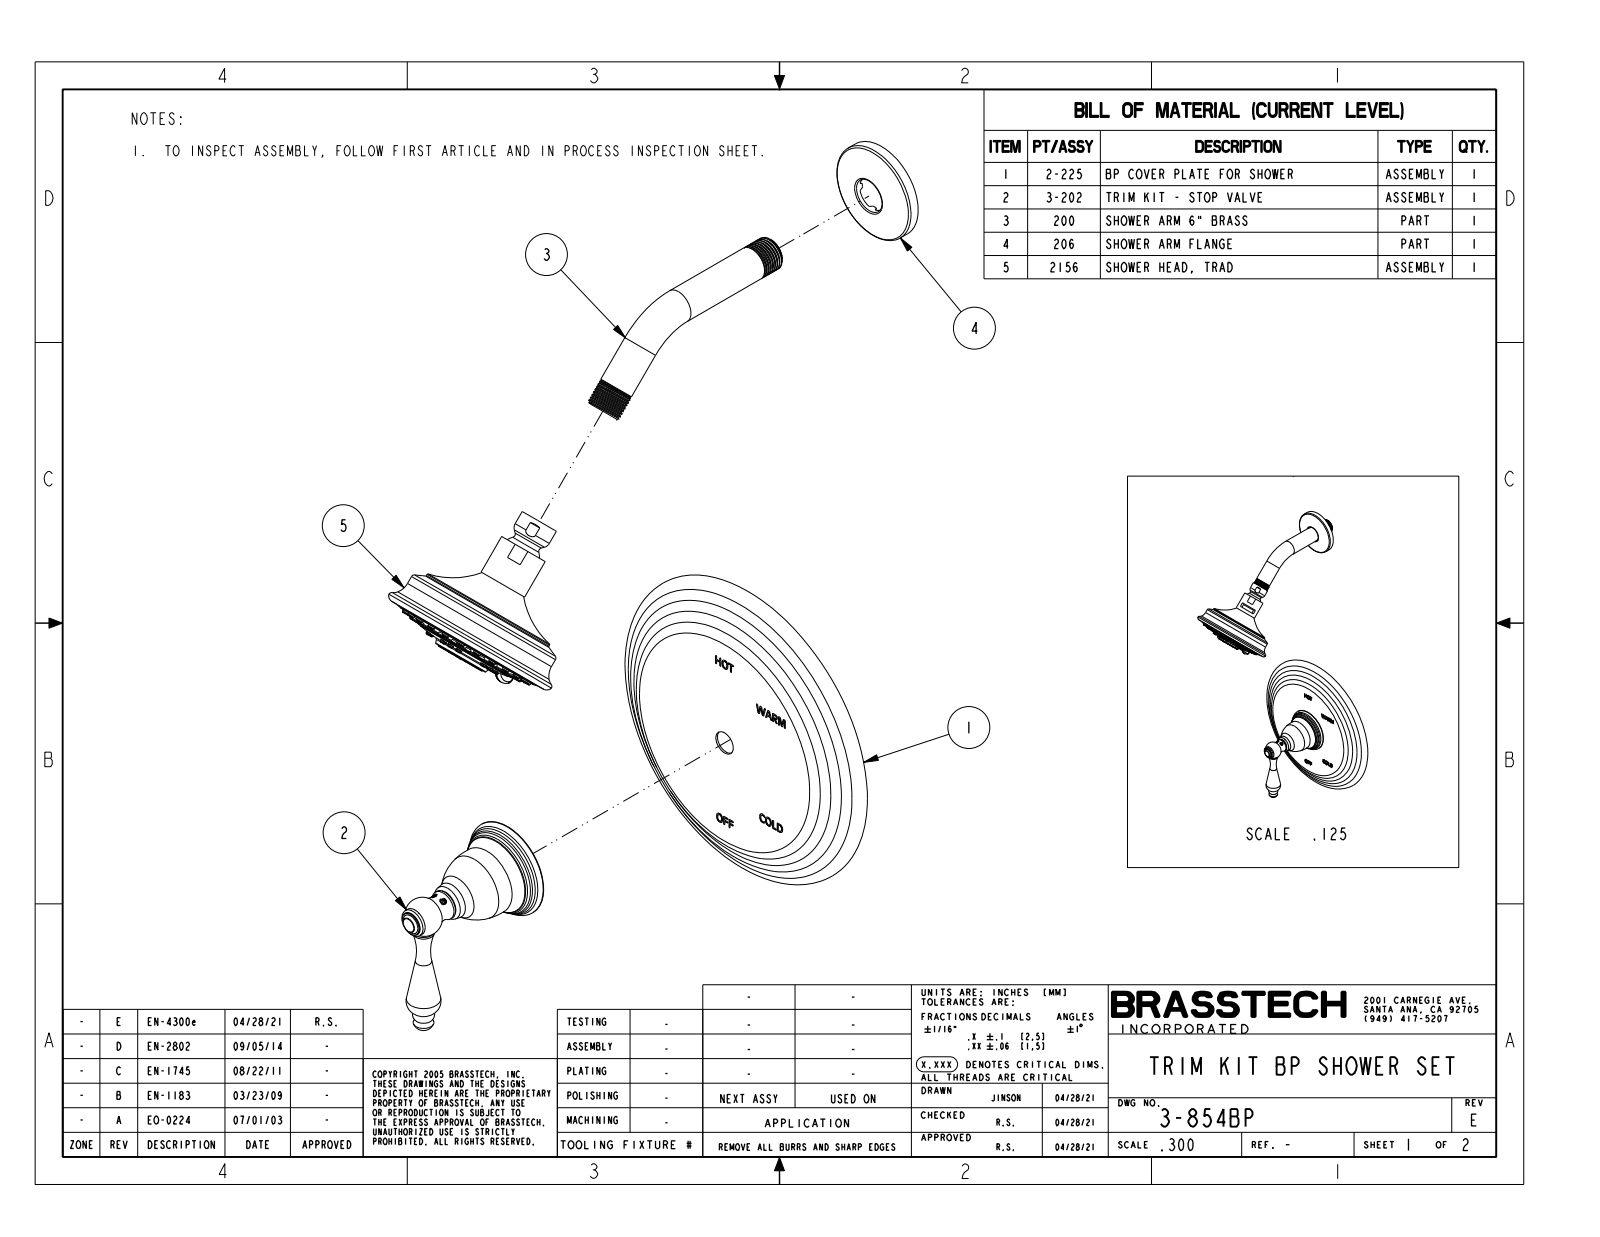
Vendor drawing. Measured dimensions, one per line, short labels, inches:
name: 3-854BP
written by: CREO PARAMETRIC BY PTC INC, 2018400 (CONFIG_CONTROL_DESIGN)
unit: in
bodies: 2 solids, 1333 faces (260 planar, 204 cylindrical, 869 other)
size: 18.065 × 8.25 × 7.75
volume: 52.57 in³; area: 191.5 in²
holes: 8× ⌀0.059, 1× ⌀0.925
bosses: 39× ⌀0.142, 23× ⌀0.165, 2× ⌀0.813, 1× ⌀3.81, 1× ⌀3.724, 1× ⌀3.24, 1× ⌀2.38, 1× ⌀2.34
rounds: 8× R0.079, 2× R0.02, 1× R0.138, 1× R0.472, 1× R0.512, 1× R0.63
face distances: 0.754, 0.063, 0.118, 0.181, 2.881, 2.763, 2.699, 2.793, 2.039, 0.75
hole spacings: 0.443, 0.579, 0.818, 0.819, 1.069, 0.443, 0.578, 1.069
